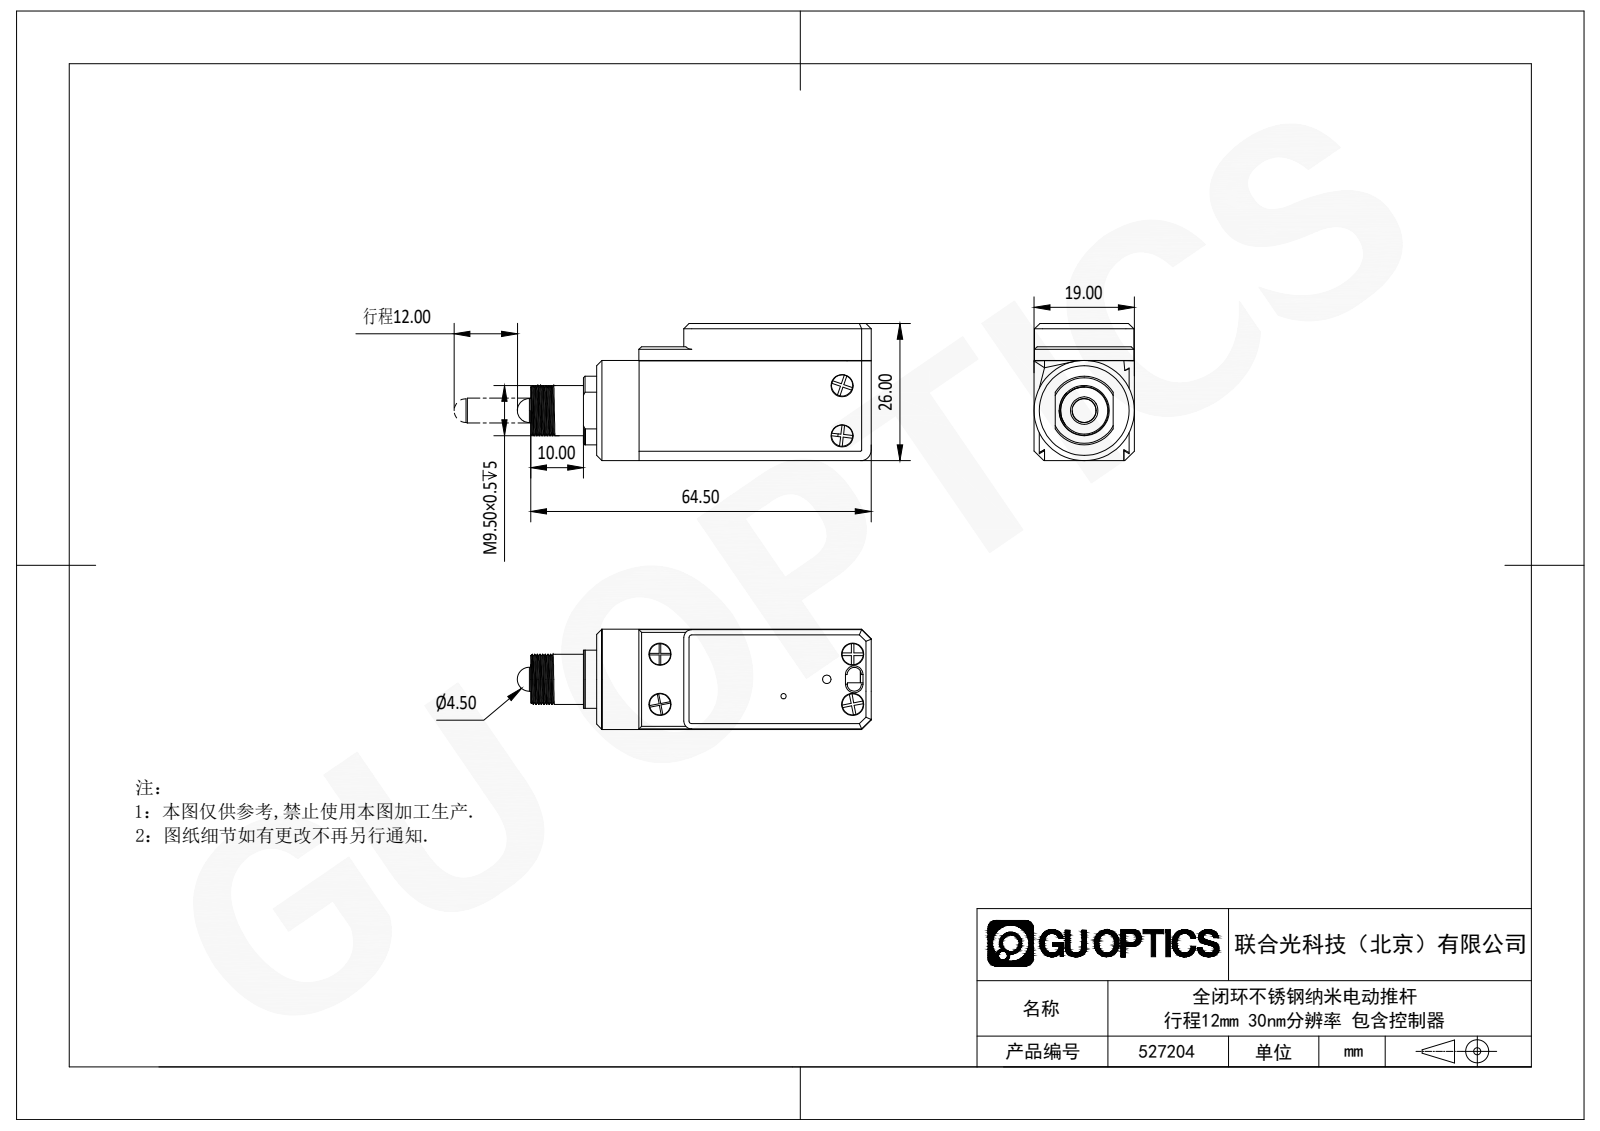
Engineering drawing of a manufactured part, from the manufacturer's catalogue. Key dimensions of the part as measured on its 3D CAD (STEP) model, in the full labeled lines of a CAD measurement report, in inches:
Part name (STEP PRODUCT): 527204
STEP written by: SolidWorks 2020 (CONFIG_CONTROL_DESIGN)
Units: inches
Bodies: 0 solids, 298 faces (199 planar, 77 cylindrical, 22 other)
Overall size (bounding box): 2.638 × 1.024 × 0.748
Round holes (diameter × count): ⌀0.157 ×3, ⌀0.165 ×2, ⌀0.374 ×1, ⌀0.748 ×1
Round bosses / shafts (diameter × count): ⌀0.165 ×7, ⌀0.157 ×3, ⌀0.205 ×1, ⌀0.098 ×1, ⌀0.063 ×1, ⌀0.039 ×1
Partial cylindrical surfaces — rounded edges, fillets, slot ends (radius × count): R0.059 ×6, R0.079 ×2, R0.083 ×1, R0.256 ×1
Main face-to-face distances: 0.039, 0.748, 0.669, 0.744, 0.709, 0.079, 0.075, 0.63, 0.035, 0.705
Hole centre spacings: 0.286, 1.099, 0.374, 0.866
